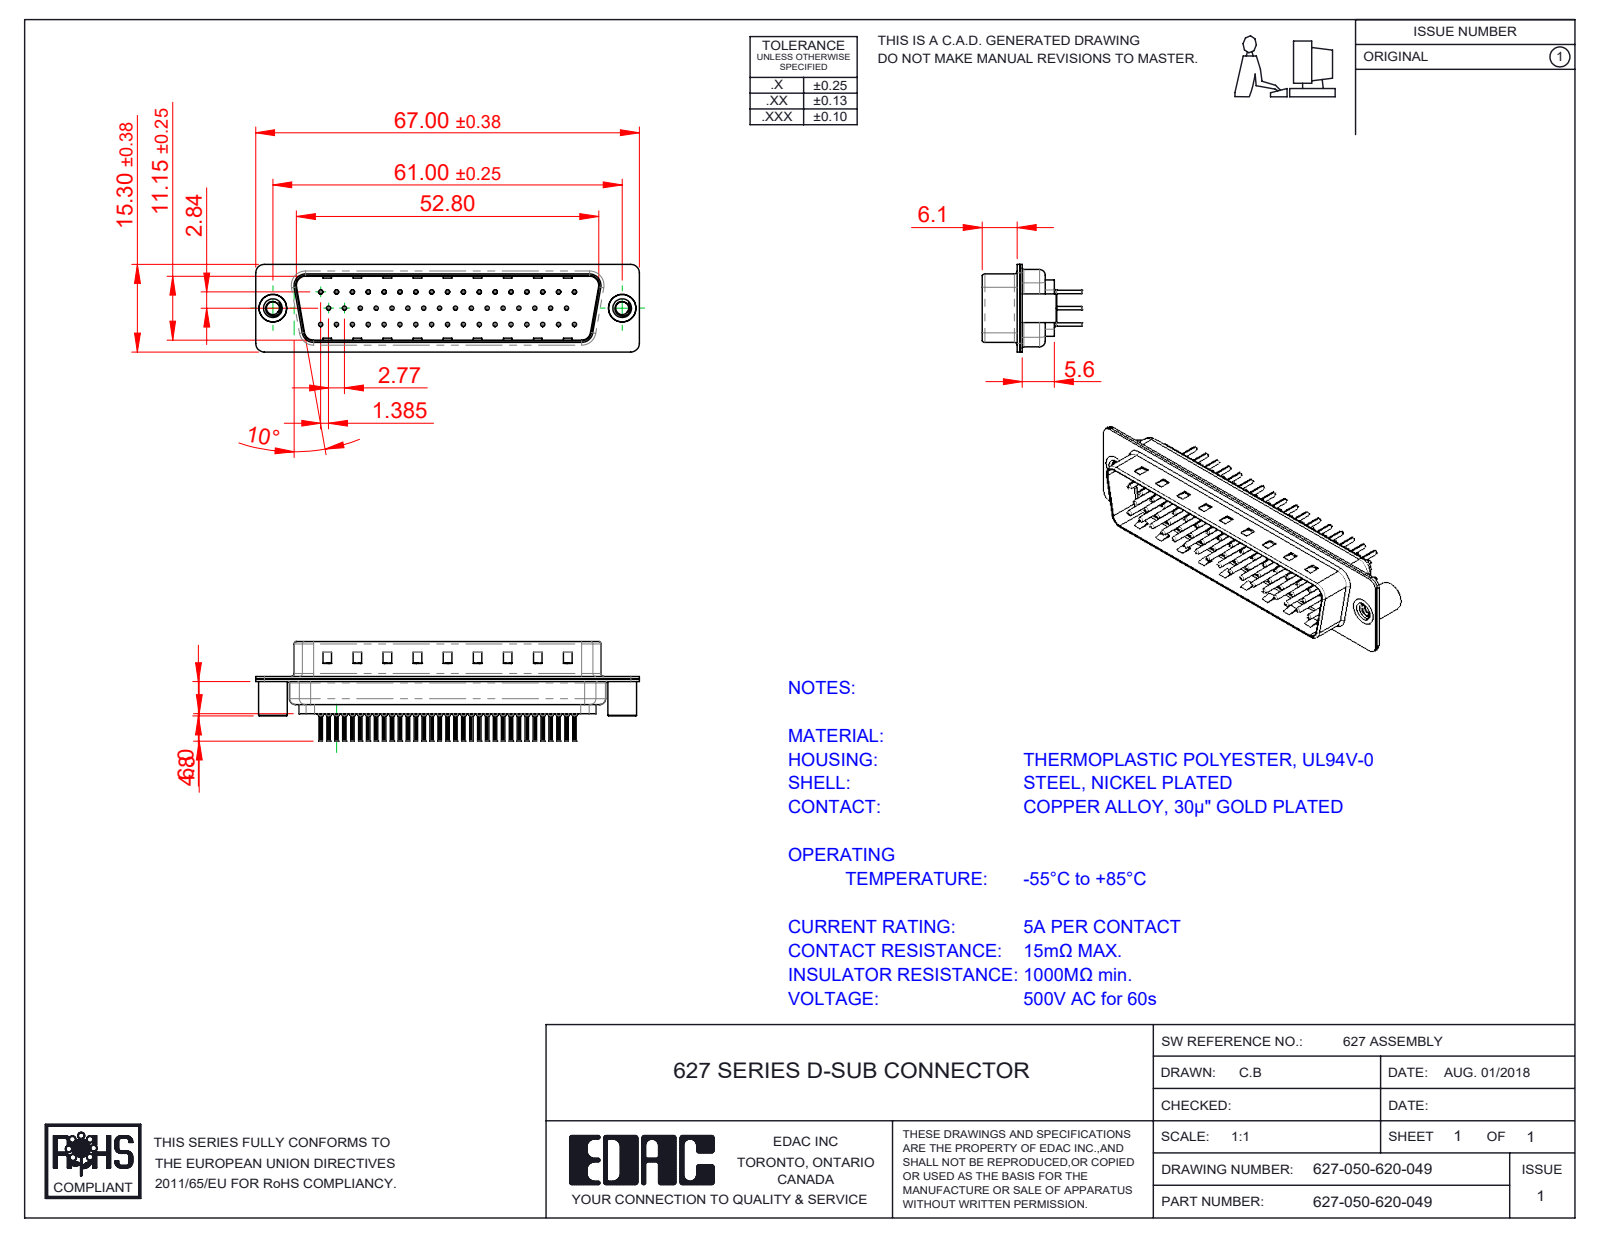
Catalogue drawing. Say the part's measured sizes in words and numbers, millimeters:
The part is named "627-050-620-049; 627 Contact Row 1_20L; 627 Housing_50 LP; 627 Contact Row 3_20L (+4 more)". Its 3-D file was written by "SolidWorks 2020 (CONFIG_CONTROL_DESIGN)". It is 55 solids with 5334 faces: 1403 planar, 2011 cylindrical and 1920 other. Overall it measures 67 by 17.3 by 15.3 millimeters. Its volume is 4 520 cubic millimeters and its surface area 12 775 square millimeters. Round holes: 50 of diameter 0.2, 50 of diameter 0.35, 50 of diameter 1.1, 50 of diameter 1.6, 2 of diameter 2.26, 2 of diameter 4, 2 of diameter 4.8. Round bosses or shafts: 50 of diameter 2, 50 of diameter 1.5, 50 of diameter 0.75, 50 of diameter 0.6, 2 of diameter 5, 2 of diameter 4.9. Partial cylindrical surfaces (rounded edges, fillets, slot ends): 100 of radius 0.1, 16 of radius 1.5, 12 of radius 2, 8 of radius 0.5, 8 of radius 1.6, 4 of radius 0.25, 4 of radius 0.6, 4 of radius 0.65. The main face-to-face distances are 0.4, 0.45, 11.55, 0.9, 6.05, 6.5, 0.78, 12.33, 1.95, 0.77. The hole center spacings are 3.16, 2.77, 5.54, 8.31, 11.08, 13.85, 16.62, 5.03.
